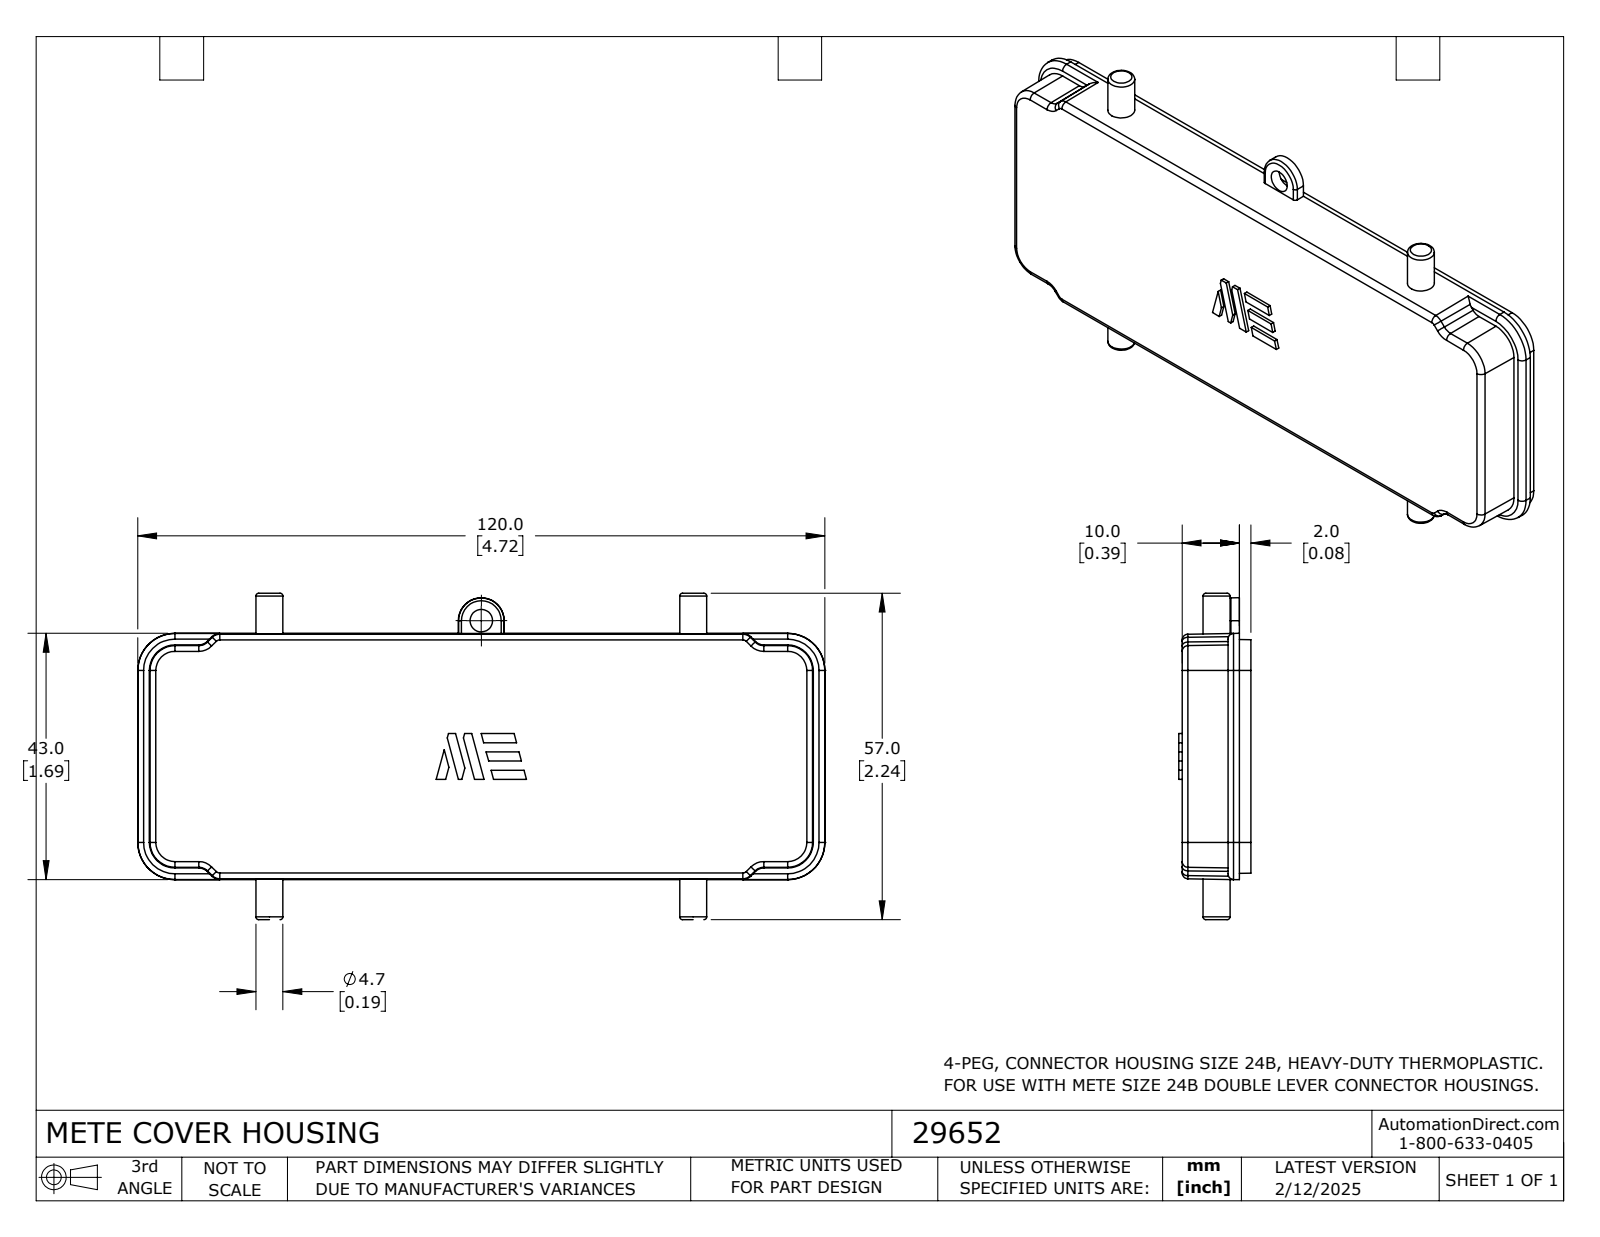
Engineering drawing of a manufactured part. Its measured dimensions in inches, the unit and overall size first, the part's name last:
Units: inches
Overall size (bounding box): 4.724 × 2.244 × 0.496
Round bosses / shafts (diameter × count): ⌀0.185 ×2
Partial cylindrical surfaces — rounded edges, fillets, slot ends (radius × count): R0.039 ×14, R0.02 ×12
Main face-to-face distances: 0.079, 0.102, 0.394, 0.315, 0.067, 0.472, 1.65, 1.547, 0.043, 0.024
Volume: 1.037 in³ · Surface area: 26.46 in²
Bodies: 1 solid, 196 faces (80 planar, 40 cylindrical, 76 other)
Part name (STEP PRODUCT): 29652
STEP written by: SolidWorks 2024 (CONFIG_CONTROL_DESIGN)
